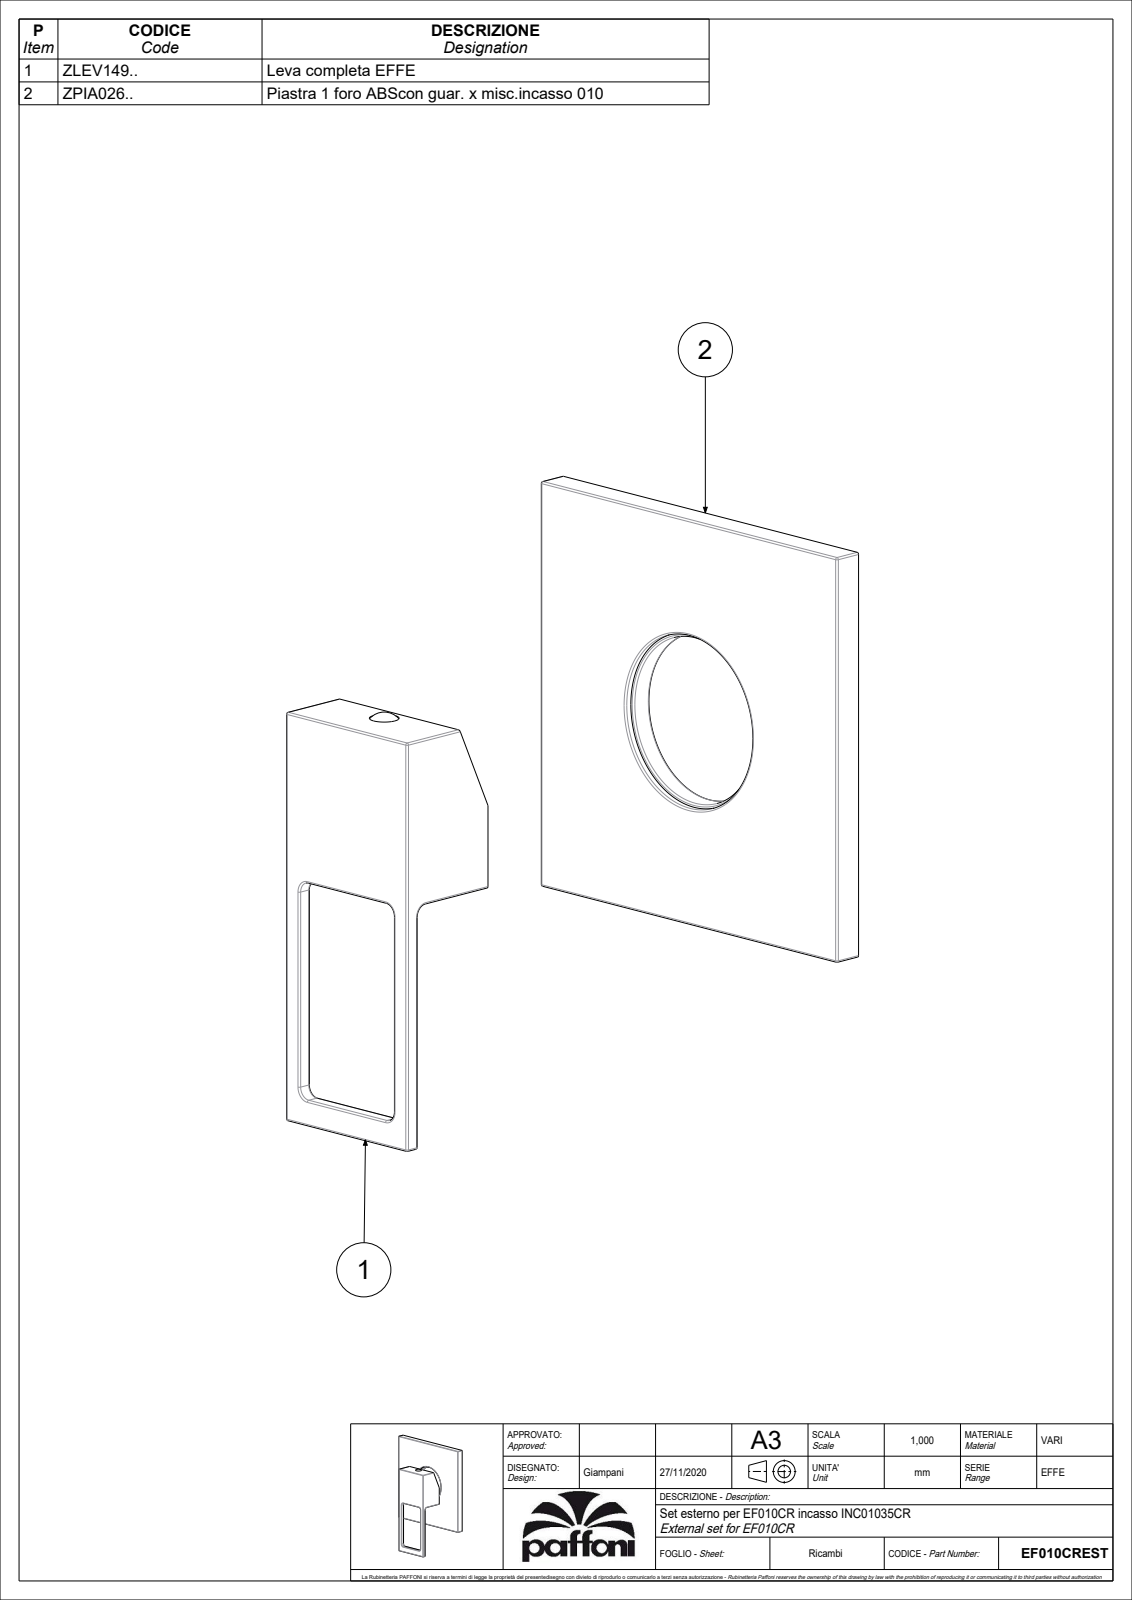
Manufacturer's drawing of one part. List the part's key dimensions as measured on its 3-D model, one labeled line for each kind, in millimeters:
Part name (STEP PRODUCT): EF010CREST
STEP written by: CREO PARAMETRIC BY PTC INC, 2020044 (CONFIG_CONTROL_DESIGN)
Units: millimetres
Bodies: 2 solids, 210 faces (81 planar, 83 cylindrical, 46 other)
Overall size (bounding box): 143.5 × 110 × 40
Volume: 77 798 mm³ · Surface area: 50 443 mm²
Round holes (diameter × count): ⌀3 ×1, ⌀4.5 ×1, ⌀5.5 ×1, ⌀7.8 ×1, ⌀45 ×1, ⌀47 ×1, ⌀49 ×1
Round bosses / shafts (diameter × count): ⌀51 ×1, ⌀7.6 ×1, ⌀5 ×1
Partial cylindrical surfaces — rounded edges, fillets, slot ends (radius × count): R0.5 ×36, R3 ×5, R1 ×4, R2 ×4, R4 ×1
Main face-to-face distances: 7, 2, 32.5, 77.5, 30, 5, 32, 39, 36, 34
